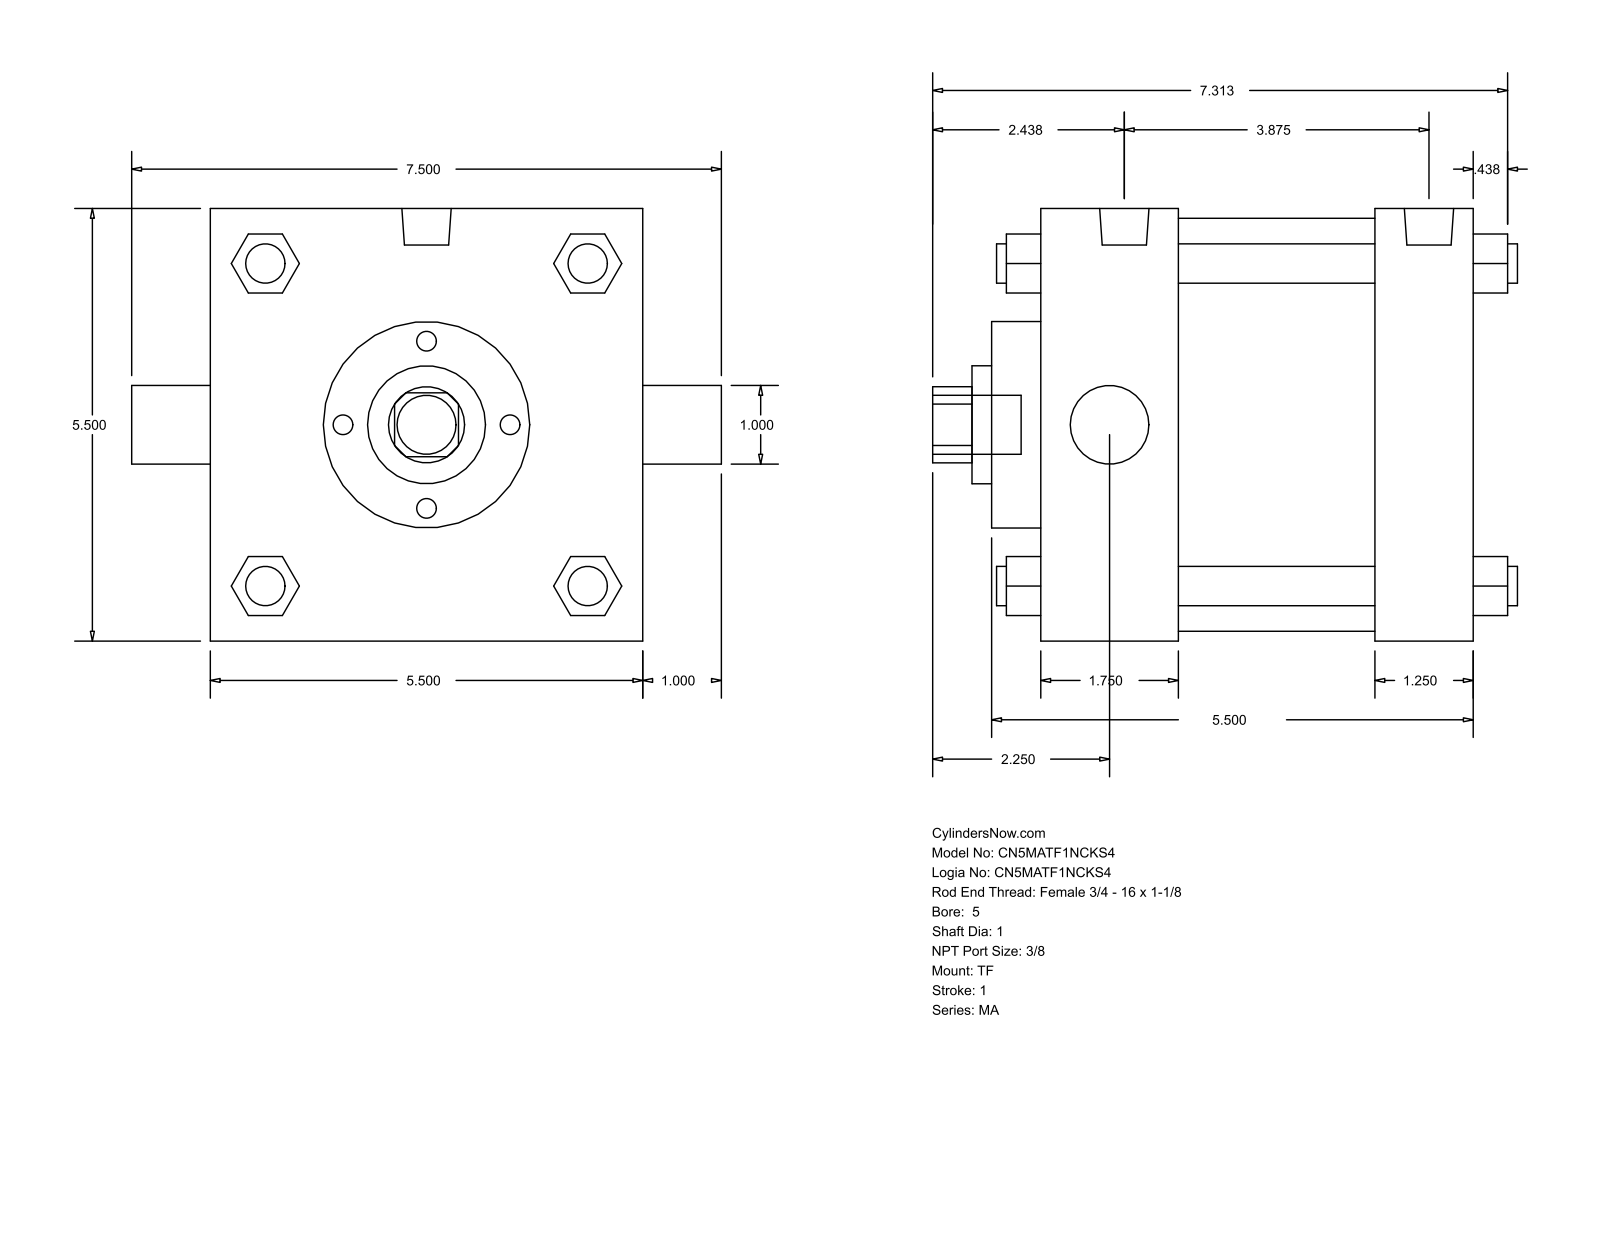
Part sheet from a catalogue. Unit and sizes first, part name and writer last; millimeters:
Units: millimetres
Overall size (bounding box): 190.5 × 188.91 × 139.7
Round holes (diameter × count): ⌀25.4 ×2, ⌀38.1 ×1, ⌀66.67 ×1, ⌀133.35 ×1
Round bosses / shafts (diameter × count): ⌀12.7 ×4, ⌀11.11 ×3, ⌀15.93 ×2, ⌀19.05 ×1
Partial cylindrical surfaces — rounded edges, fillets, slot ends (radius × count): R12.29 ×1
Main face-to-face distances: 139.7, 107.96, 31.74, 44.46, 63.5, 95.24, 15.87, 60.33, 123.83, 155.57
Bodies: 0 solids, 122 faces (93 planar, 29 cylindrical, 0 other)
Part name (STEP PRODUCT): MA_TF__0500_1
STEP written by: GSSL Pune (CONFIG_CONTROL_DESIGN)
